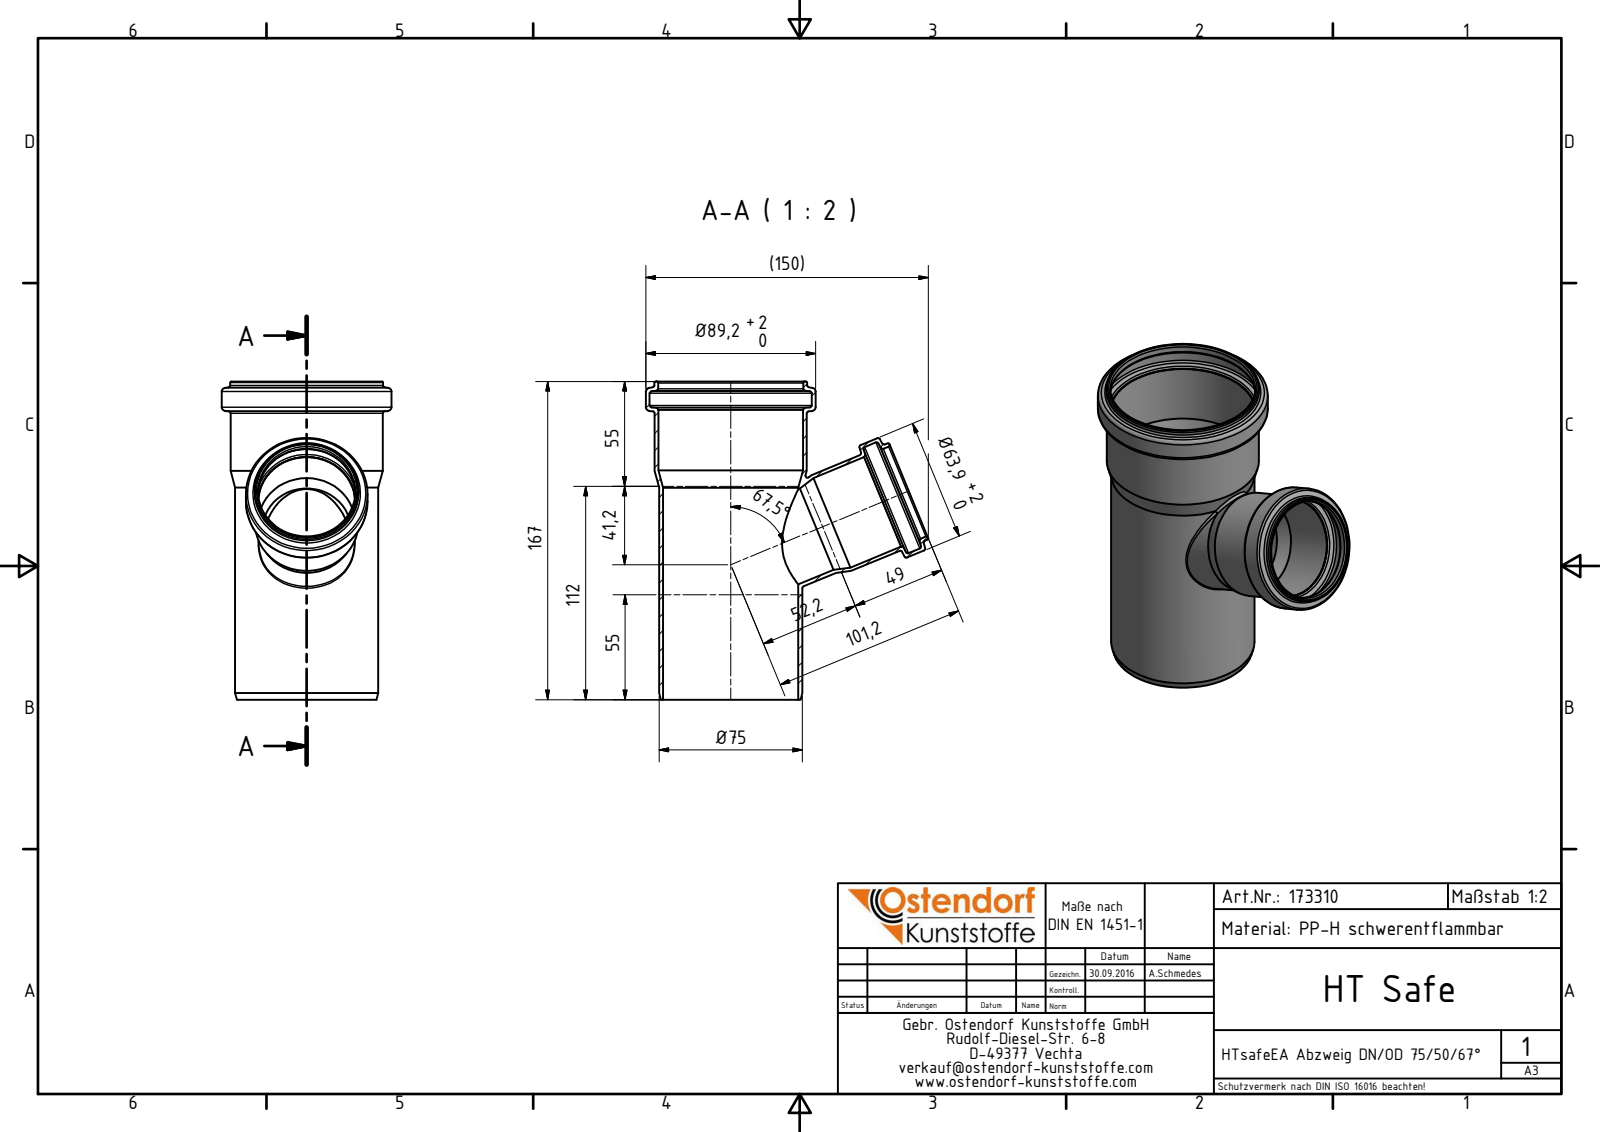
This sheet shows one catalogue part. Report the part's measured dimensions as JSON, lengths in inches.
{"part_name": "173310 HTsafeEA DN_OD 75_50_67°", "step_written_by": "Autodesk Inventor 2016 (AUTOMOTIVE_DESIGN)", "units": "inches", "bodies": {"solids": 1, "faces": 58, "planar": 5, "cylindrical": 18, "other": 35}, "overall_size": [6.575, 5.843, 3.512], "volume_in3": 6.332, "surface_area_in2": 160.6, "round_holes": [[2.012, 2], [1.819, 1], [2, 1], [2.374, 1], [2.795, 1], [2.988, 1], [3, 1], [3.354, 1]], "round_bosses_or_shafts": [[3.512, 1], [3.157, 1], [3.146, 1], [2.961, 1], [2.516, 1], [2.154, 1], [2.142, 1], [1.976, 1]], "face_to_face_distances": [6.575, 5.989, 0.586, 0.587]}
